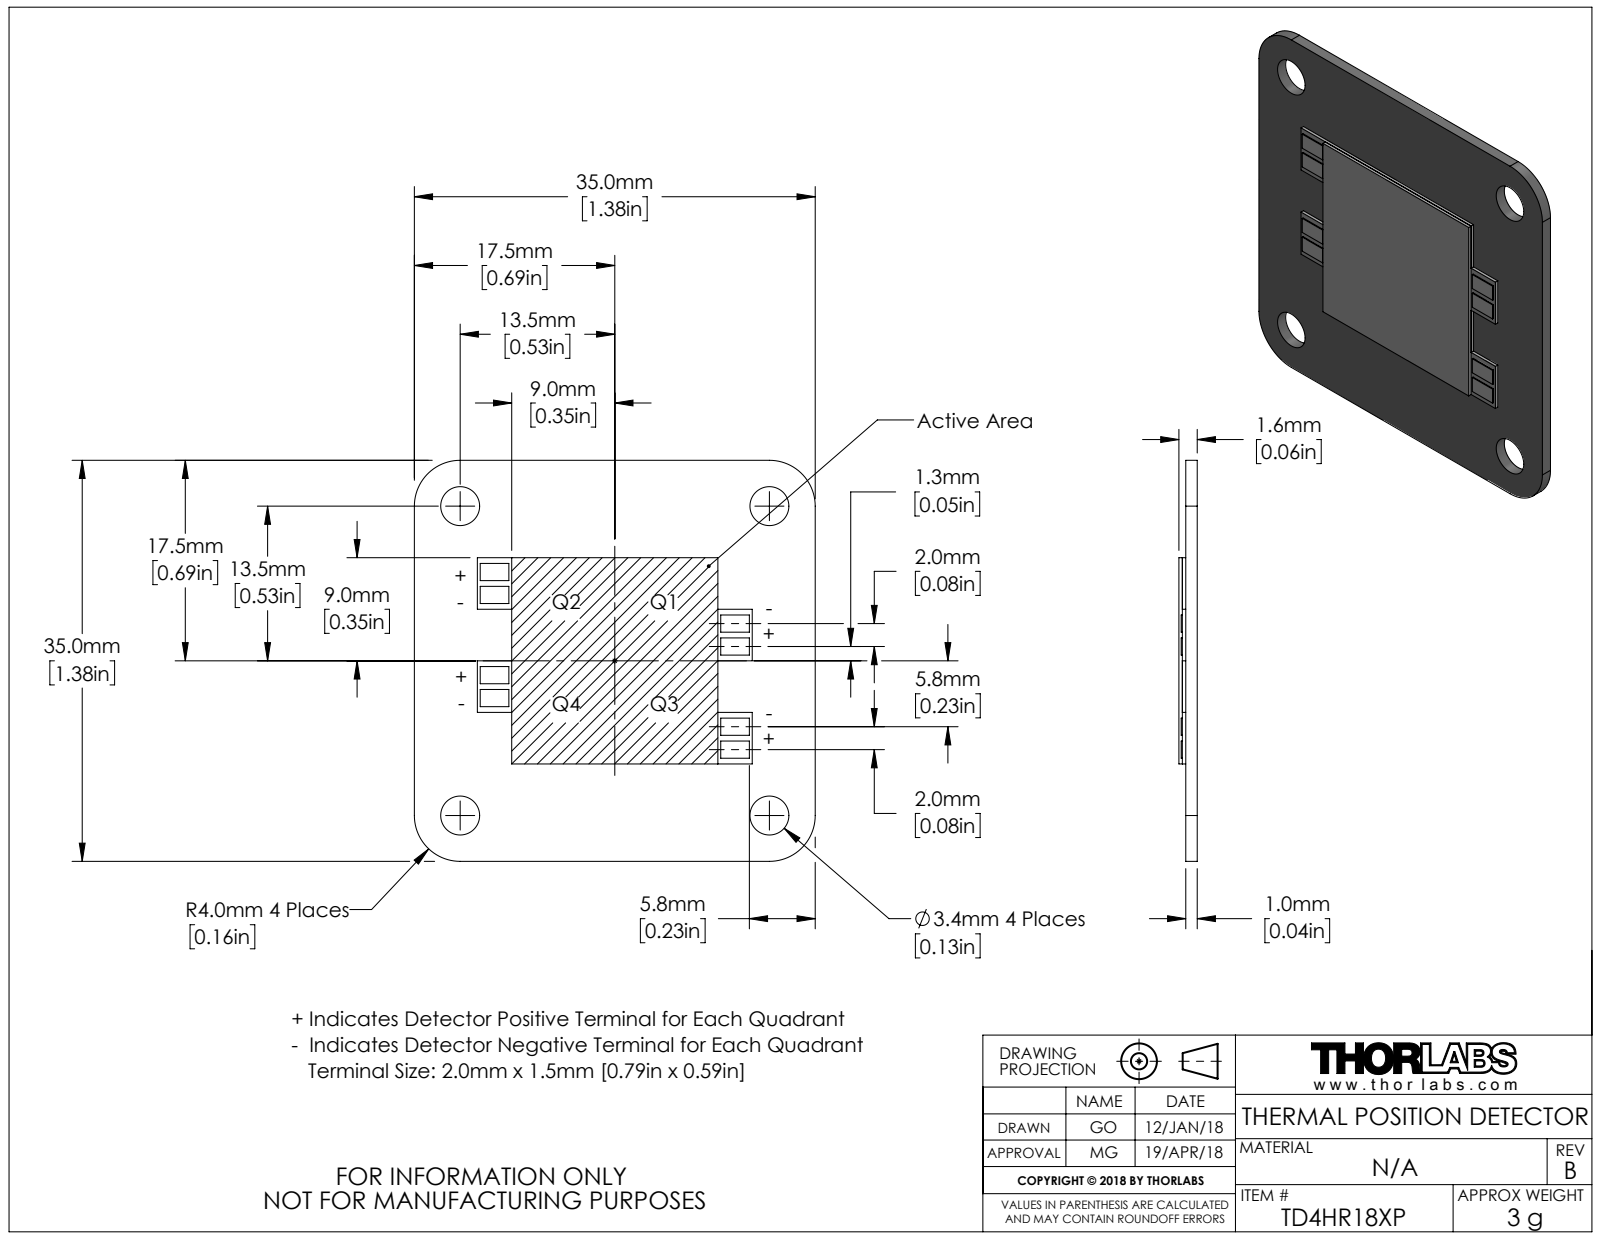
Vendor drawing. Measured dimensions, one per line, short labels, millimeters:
name: MTN11039-E0W
written by: SolidWorks 2016 (CONFIG_CONTROL_DESIGN)
unit: mm
bodies: 2 solids, 81 faces (69 planar, 12 cylindrical, 0 other)
size: 35 × 35 × 1.6
volume: 1 389 mm³; area: 3 231 mm²
holes: 4× ⌀3.4
rounds: 4× R4
face distances: 1, 1.3, 1.6, 0.6, 35, 8.5, 26.5, 1.4, 0.4, 18
hole spacings: 27, 38.18
